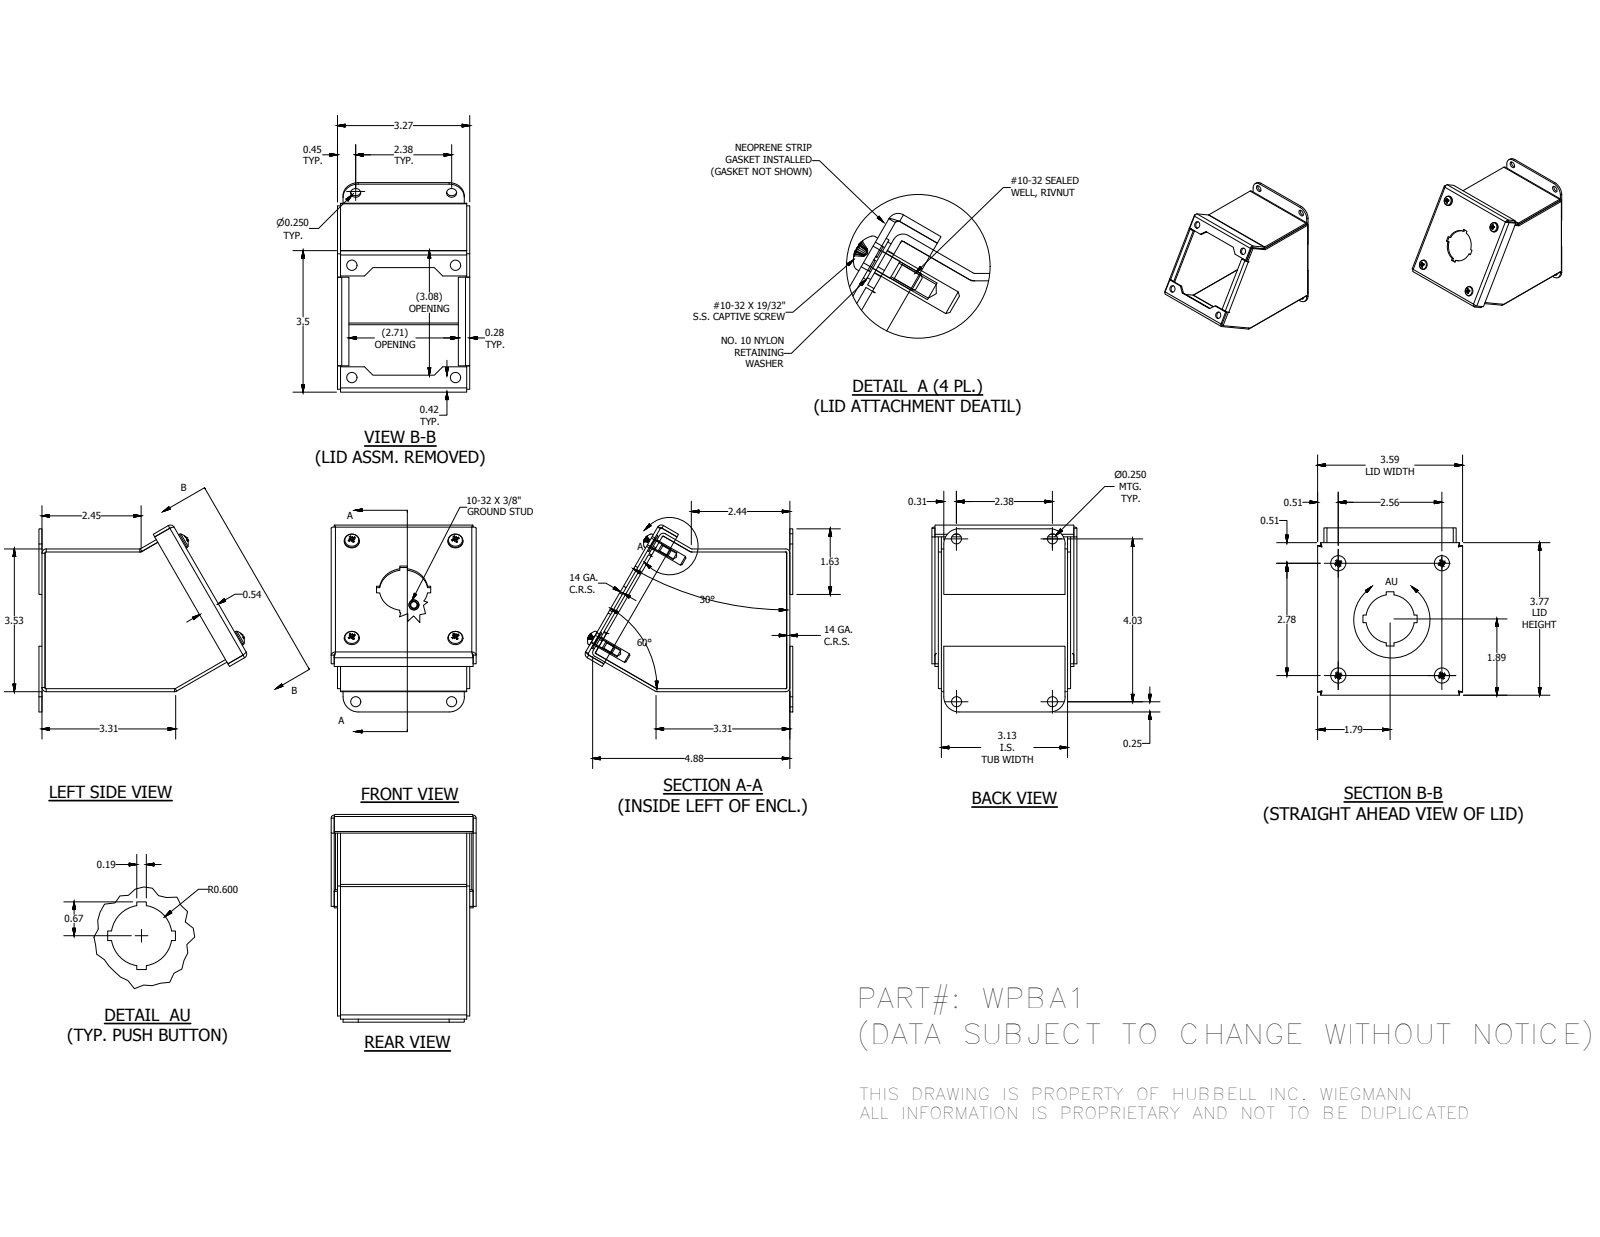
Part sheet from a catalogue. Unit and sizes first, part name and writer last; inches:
Units: inches
Overall size (bounding box): 5.141 × 4.623 × 3.587
Round holes (diameter × count): ⌀0.156 ×4, ⌀0.196 ×4, ⌀0.25 ×4, ⌀0.257 ×4, ⌀0.278 ×4, ⌀0.281 ×4, ⌀1.2 ×1
Round bosses / shafts (diameter × count): ⌀0.19 ×5, ⌀0.453 ×4, ⌀0.406 ×4, ⌀0.373 ×4, ⌀0.248 ×4, ⌀0.25 ×1
Partial cylindrical surfaces — rounded edges, fillets, slot ends (radius × count): R0.031 ×12, R0.105 ×12, R0.089 ×4, R0.375 ×4
Main face-to-face distances: 0.074, 0.074, 3.456, 3.125, 3.199, 3.273, 3.199, 0.148, 3.382, 3.53
Hole centre spacings: 2.562, 2.563, 2.749, 2.777, 0.028, 1.879, 2.376, 3.757
Volume: 7.306 in³ · Surface area: 208.6 in²
Bodies: 19 solids, 480 faces (287 planar, 94 cylindrical, 99 other)
Part name (STEP PRODUCT): WPBA1BKP; WPBA1ROWEWPR; WPBA1ROWEWPL; 34984 (+6 more)
STEP written by: Autodesk Inventor 2014 (AUTOMOTIVE_DESIGN)
